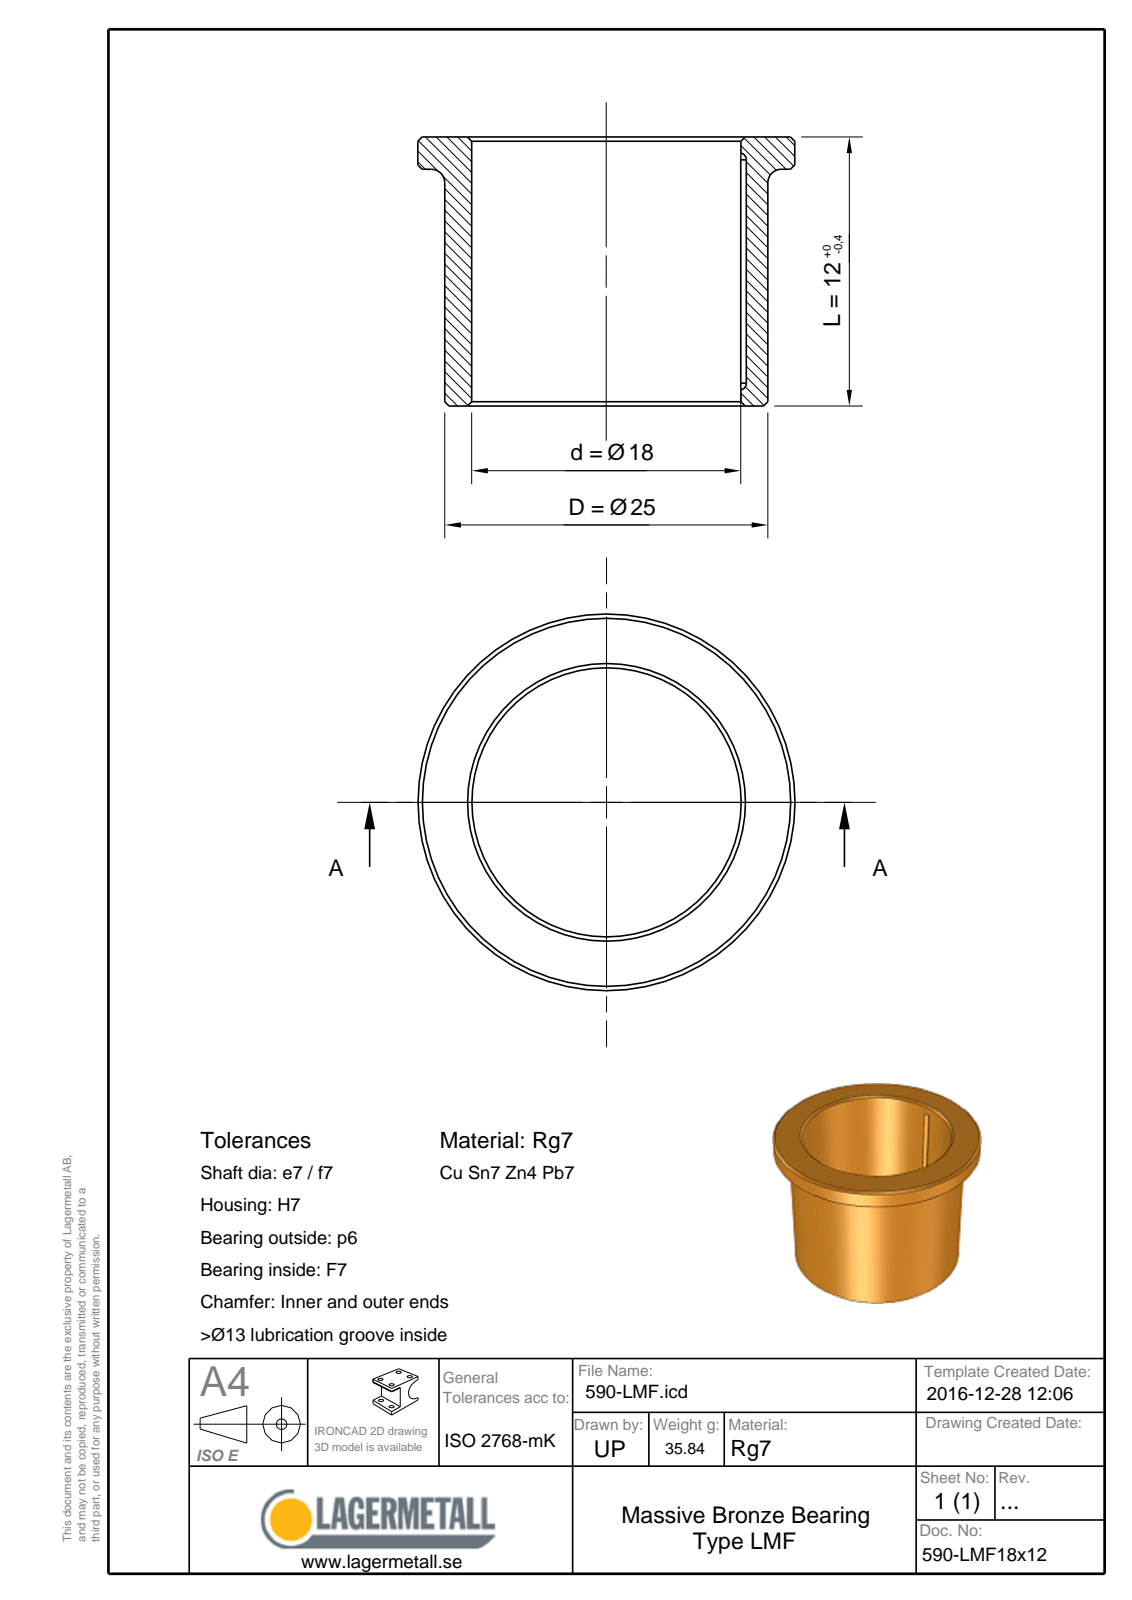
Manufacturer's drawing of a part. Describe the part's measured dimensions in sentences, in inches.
The part is named "590-LMF18x12". Its 3-D file was written by "Spatial InterOp 3D (CONFIG_CONTROL_DESIGN)". It is 1 solid with 19 faces: 5 planar, 6 cylindrical and 8 other. Overall it measures 1.26 by 1.26 by 0.472 inches. Its volume is 0.249 cubic inches and its surface area 4.112 square inches. Round holes: 1 of diameter 0.709. Round bosses or shafts: 1 of diameter 1.26, 1 of diameter 0.984. Partial cylindrical surfaces (rounded edges, fillets, slot ends): 3 of radius 0.03. The main face-to-face distances are 0.472, 0.315, 0.157, 0.059.
